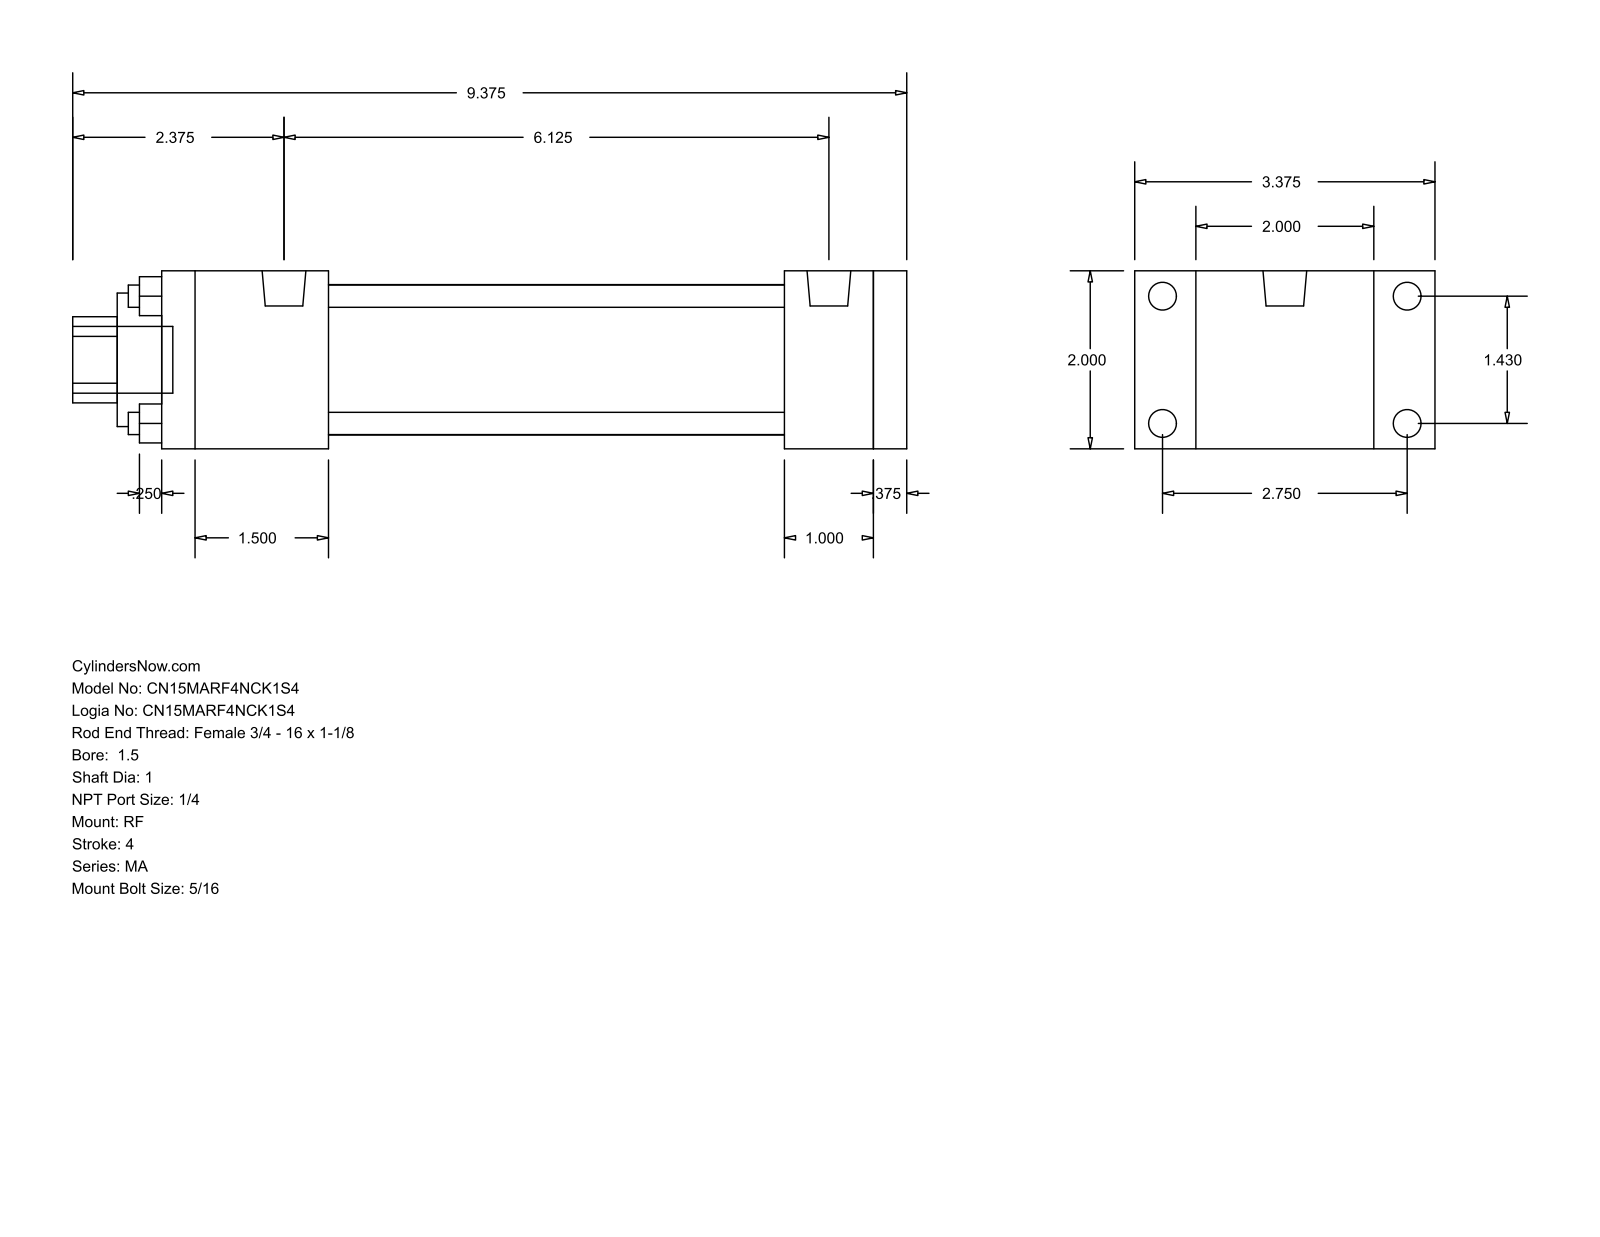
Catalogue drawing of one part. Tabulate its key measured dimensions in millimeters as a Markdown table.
| quantity | value |
| --- | --- |
| part name | MA_RF__0150_1 |
| STEP written by | GSSL Pune (CONFIG_CONTROL_DESIGN) |
| units | millimeters |
| bodies | 0 solids, 92 faces (64 planar, 28 cylindrical, 0 other) |
| overall size | 238.12 × 85.72 × 50.8 |
| round holes (diameter × count) | 6.35 × 4, 25.4 × 1, 38.1 × 1, 42.93 × 1 |
| round bosses / shafts (diameter × count) | 7.94 × 8, 12.49 × 2, 19.05 × 1 |
| partial cylindrical surfaces (radius × count) | 12.29 × 1 |
| main face-to-face distances | 50.8, 9.52, 212.72, 203.2, 25.4, 177.8, 34.92, 47.63, 130.17, 155.57 |
| hole center spacings | 25.68, 36.32, 51.36 |
